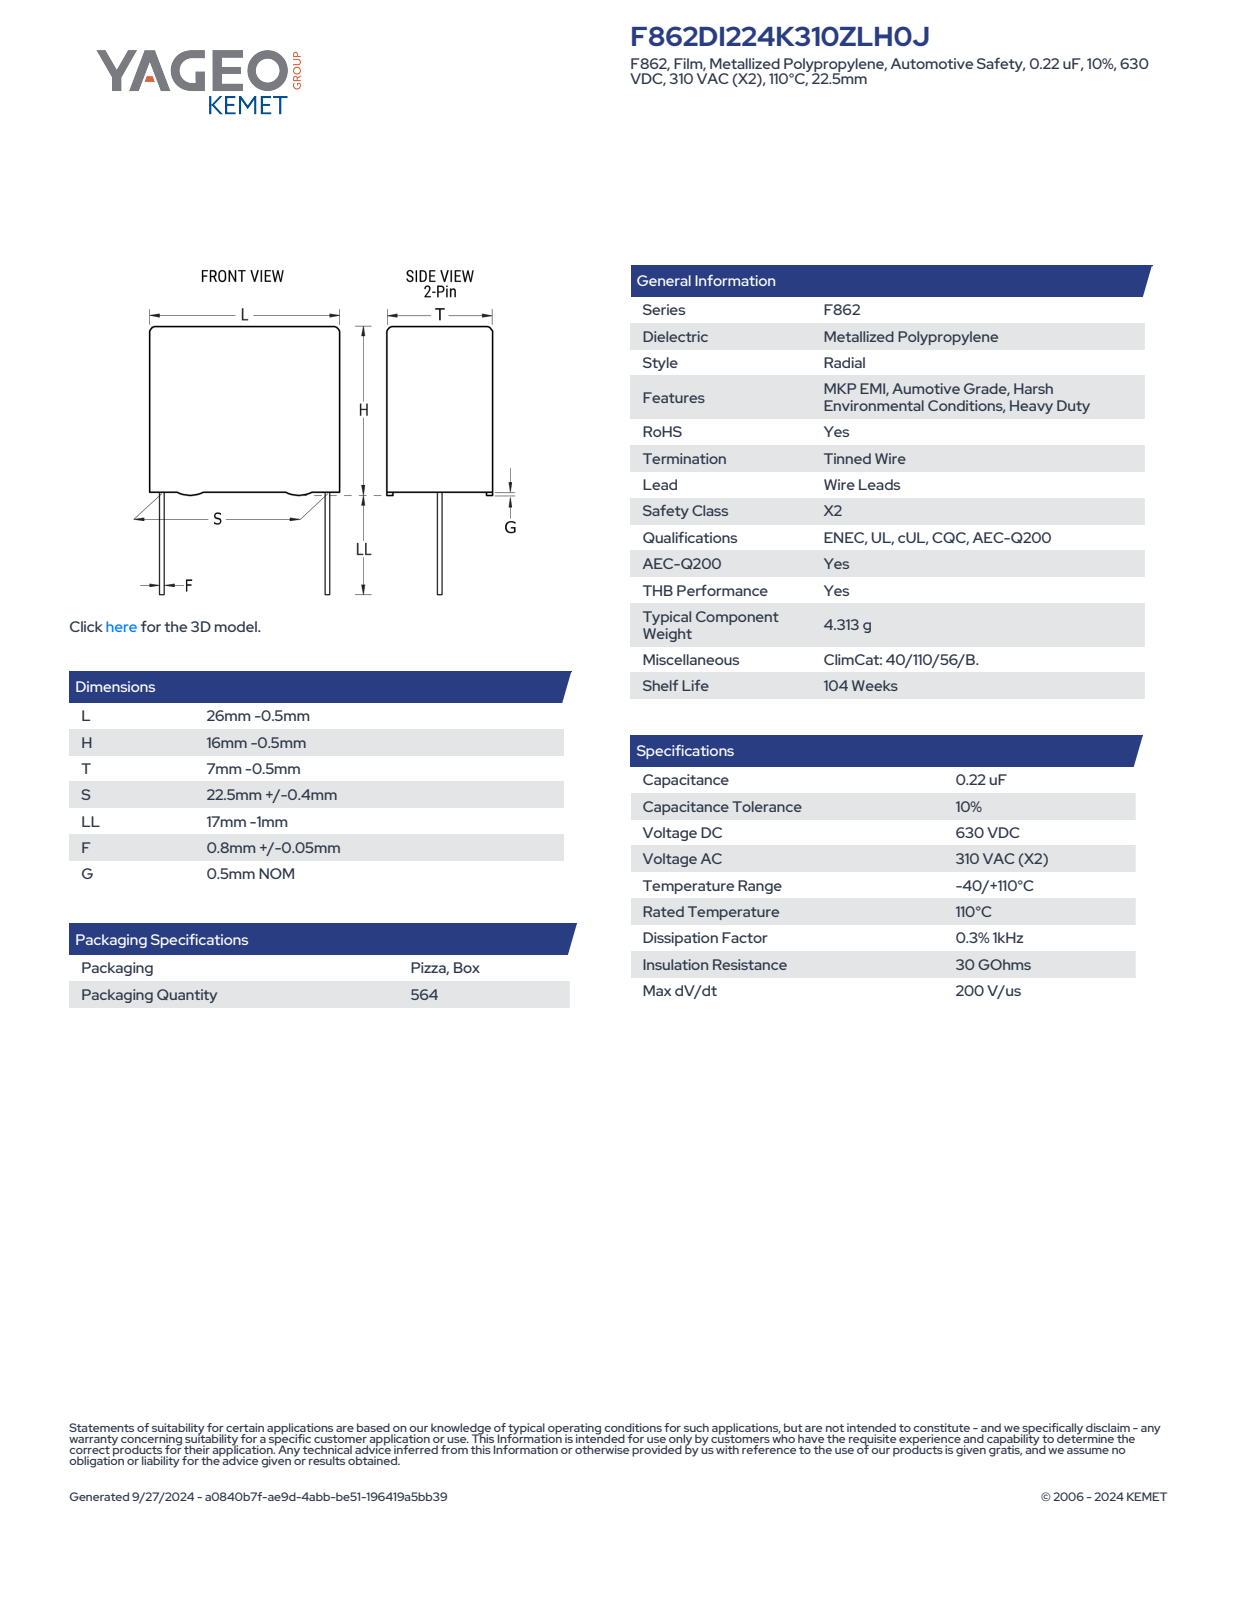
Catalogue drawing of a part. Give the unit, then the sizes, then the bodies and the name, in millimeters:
Units: millimetres
Overall size (bounding box): 31.5 × 25.5 × 6.5
Round bosses / shafts (diameter × count): ⌀0.85 ×2
Partial cylindrical surfaces — rounded edges, fillets, slot ends (radius × count): R0.5 ×4
Main face-to-face distances: 6.5, 15, 25.5, 0.37, 6.13, 0.5, 15.5, 5.76, 16, 16.5
Volume: 2 505 mm³ · Surface area: 1 453 mm²
Bodies: 4 solids, 89 faces (81 planar, 8 cylindrical, 0 other)
Part name (STEP PRODUCT): CFR_RBG_26X16X7_L25.5H15.5T6.5S22.5LL16F0.85G0.5
STEP written by: SolidWorks 2014 (AUTOMOTIVE_DESIGN)
